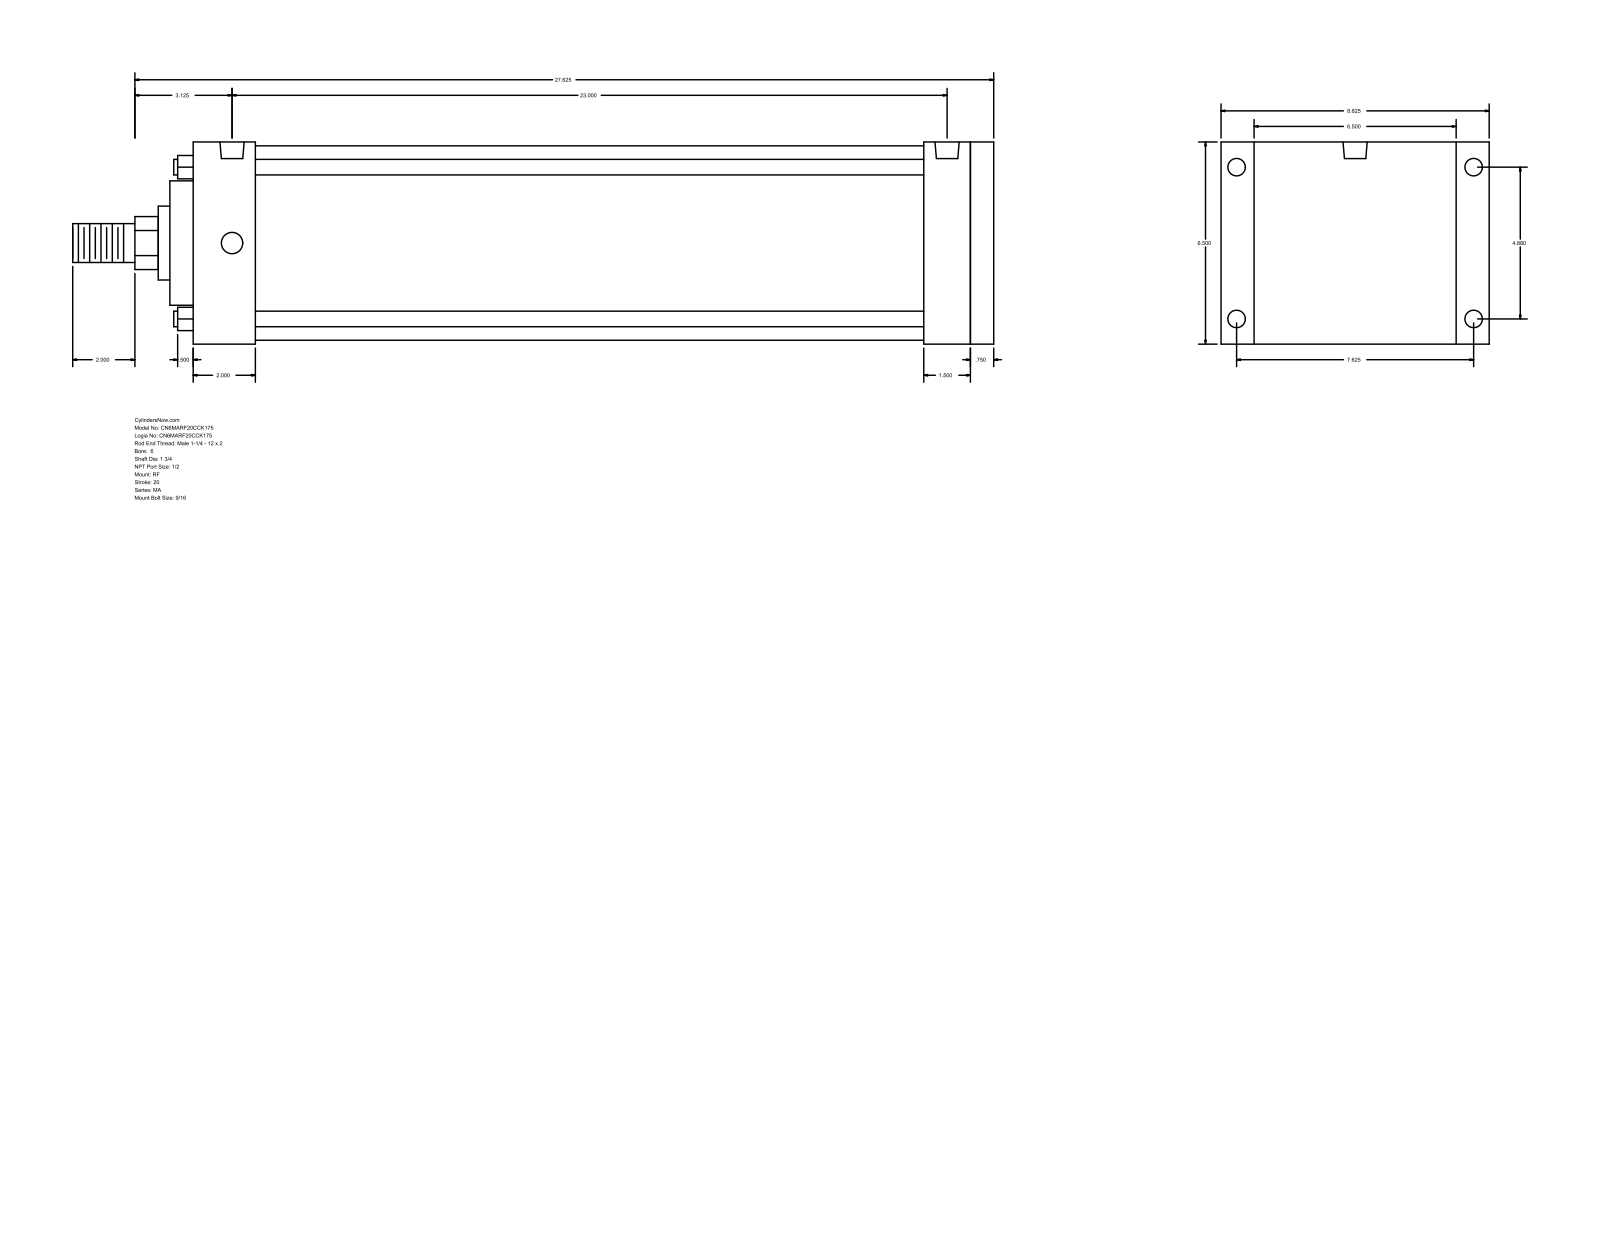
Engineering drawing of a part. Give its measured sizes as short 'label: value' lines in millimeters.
name: MA_RF__0600_1.75
written by: GSSL Pune (CONFIG_CONTROL_DESIGN)
unit: mm
bodies: 0 solids, 94 faces (65 planar, 29 cylindrical, 0 other)
size: 752.48 × 219.07 × 165.1
holes: 4× ⌀14.29, 4× ⌀17.46, 2× ⌀19.77
bosses: 4× ⌀12.7, 1× ⌀158.75, 1× ⌀101.6, 1× ⌀60.33, 1× ⌀44.45, 1× ⌀31.75
rounds: 1× R21.63
face distances: 165.1, 654.05, 19.05, 635, 38.1, 50.8, 584.2, 603.25, 596.9, 546.1
hole spacings: 123.96, 193.68, 229.95, 584.2
